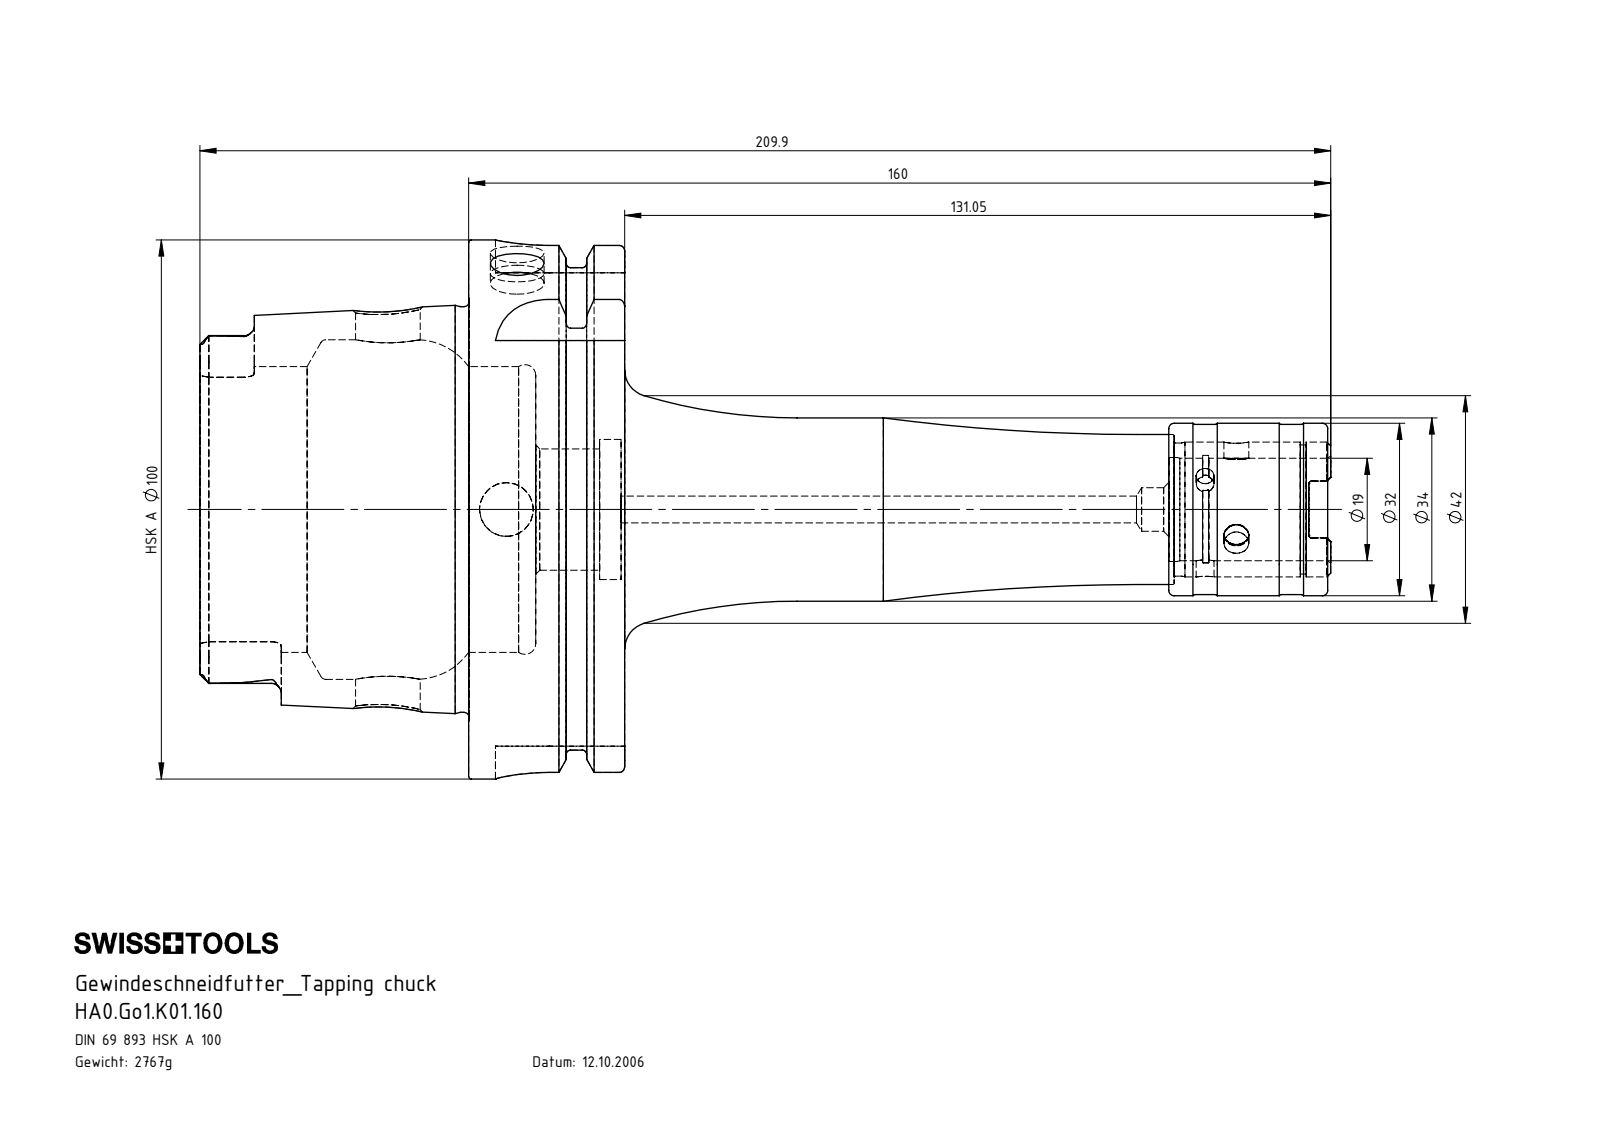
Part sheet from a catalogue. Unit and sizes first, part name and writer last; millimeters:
Units: millimetres
Overall size (bounding box): 209.9 × 100 × 100
Round holes (diameter × count): ⌀3.3 ×3, ⌀4.6 ×3, ⌀10 ×3, ⌀2 ×1, ⌀5 ×1, ⌀8 ×1, ⌀8.1 ×1, ⌀12 ×1, ⌀19 ×1, ⌀19.3 ×1, ⌀20.05 ×1, ⌀22.5 ×1
Round bosses / shafts (diameter × count): ⌀100 ×1, ⌀91.95 ×1, ⌀75.26 ×1, ⌀34 ×1, ⌀32 ×1, ⌀31.6 ×1, ⌀27.85 ×1, ⌀25 ×1
Partial cylindrical surfaces — rounded edges, fillets, slot ends (radius × count): R1.9 ×6, R4.88 ×4, R10 ×4, R2.15 ×3, R0.5 ×2
Main face-to-face distances: 28.95, 12.45, 16.5, 49.9, 62.35, 78.85, 78.2, 28.3, 15.85, 0.65
Hole centre spacings: 5.8, 151.7, 157.5
Volume: 352 390 mm³ · Surface area: 74 818 mm²
Bodies: 10 solids, 375 faces (83 planar, 122 cylindrical, 170 other)
Part name (STEP PRODUCT): HA0.Go1.K01.160; Einbausatz Go1_gespannt; Kugel Go1; Hülse Go1 (+6 more)
STEP written by: SolidWorks 2011 (AUTOMOTIVE_DESIGN)
